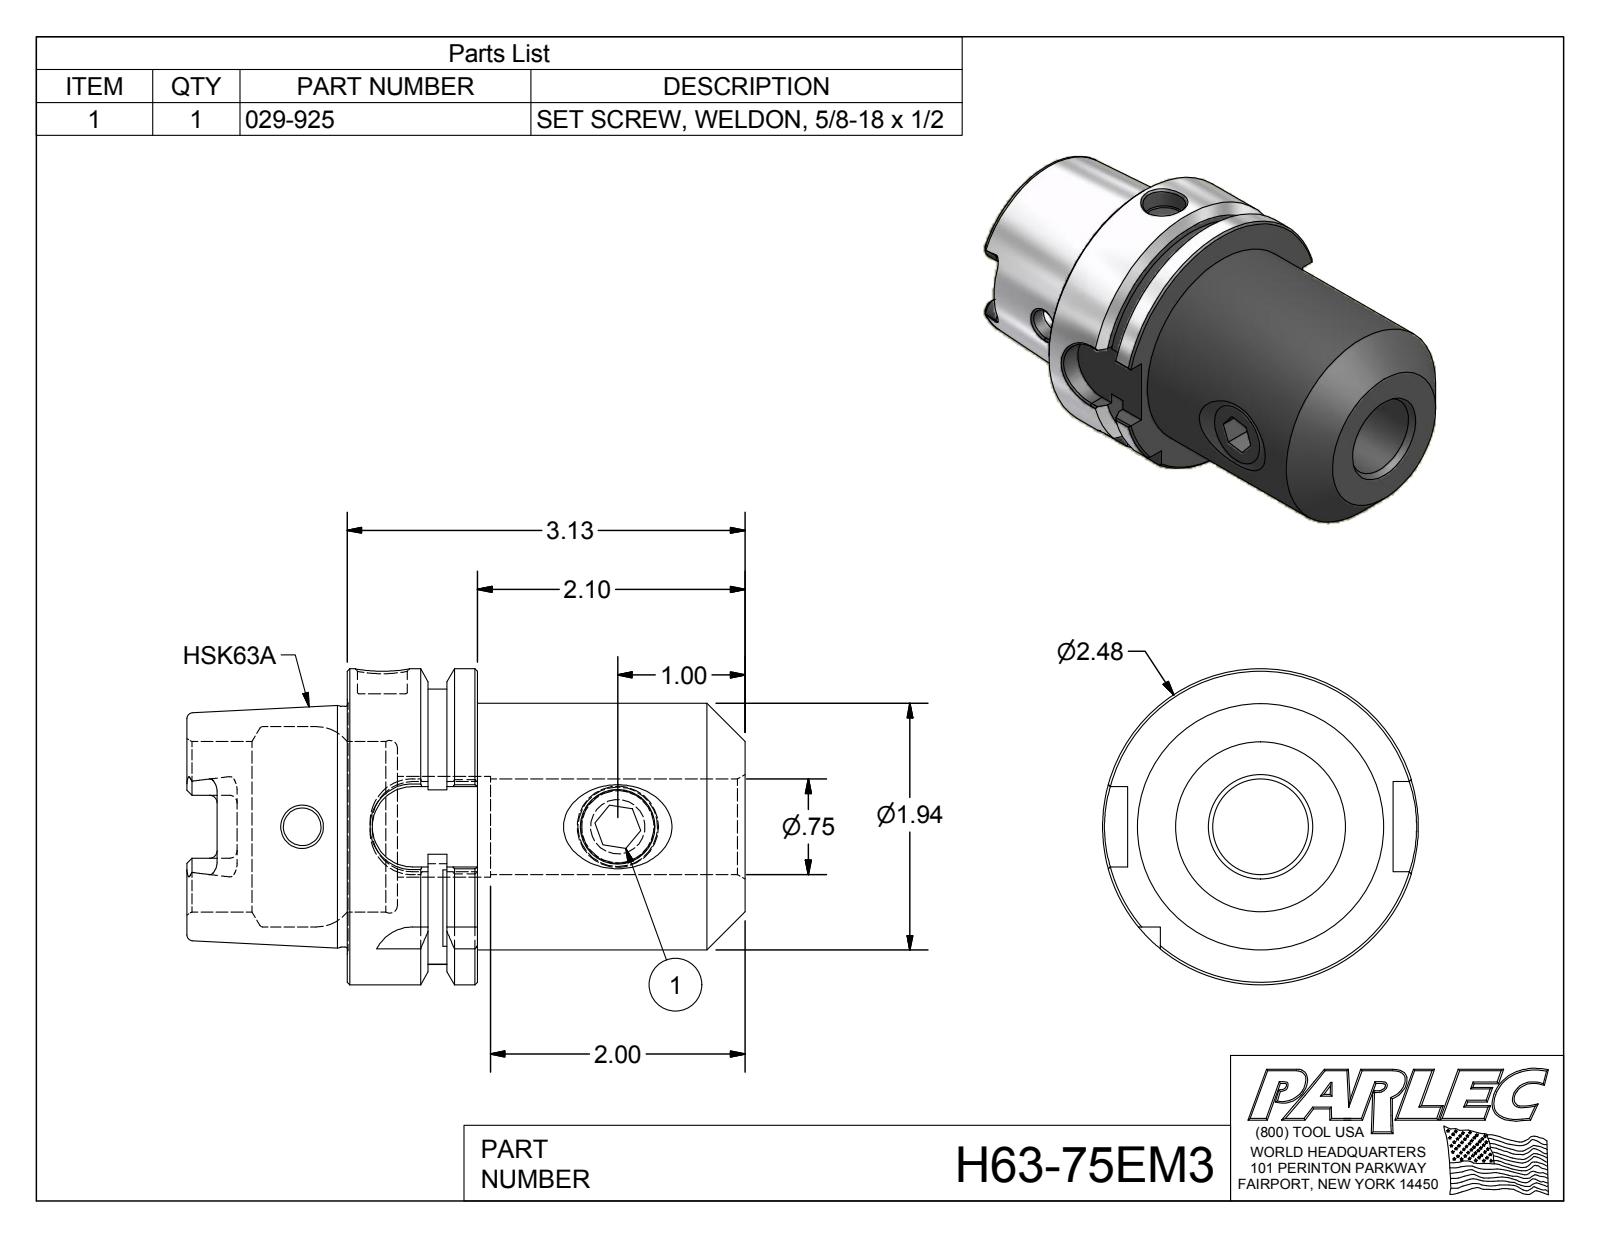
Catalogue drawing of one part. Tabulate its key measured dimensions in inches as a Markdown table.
| quantity | value |
| --- | --- |
| part name | H63-75EM3; H63-75EM3-1; 029-925 |
| STEP written by | Autodesk Inventor 2012 (AUTOMOTIVE_DESIGN) |
| units | inches |
| bodies | 2 solids, 145 faces (60 planar, 36 cylindrical, 49 other) |
| overall size | 4.385 × 2.48 × 2.48 |
| volume | 9.726 in³ |
| surface area | 53.68 in² |
| round holes (diameter × count) | 0.295 × 1, 0.394 × 1, 0.578 × 1, 0.75 × 1, 0.79 × 1, 1.339 × 1, 1.575 × 1 |
| round bosses / shafts (diameter × count) | 2.48 × 1, 1.937 × 1, 1.891 × 1, 0.625 × 1 |
| partial cylindrical surfaces (radius × count) | 0.059 × 6, 0.113 × 4, 0.315 × 4, 1.083 × 1 |
| main face-to-face distances | 1.024, 0.394, 3.125, 2.102, 0.63, 2.731, 1.26, 1.654, 2.283, 4.385 |
| hole center spacings | 2.48 |
